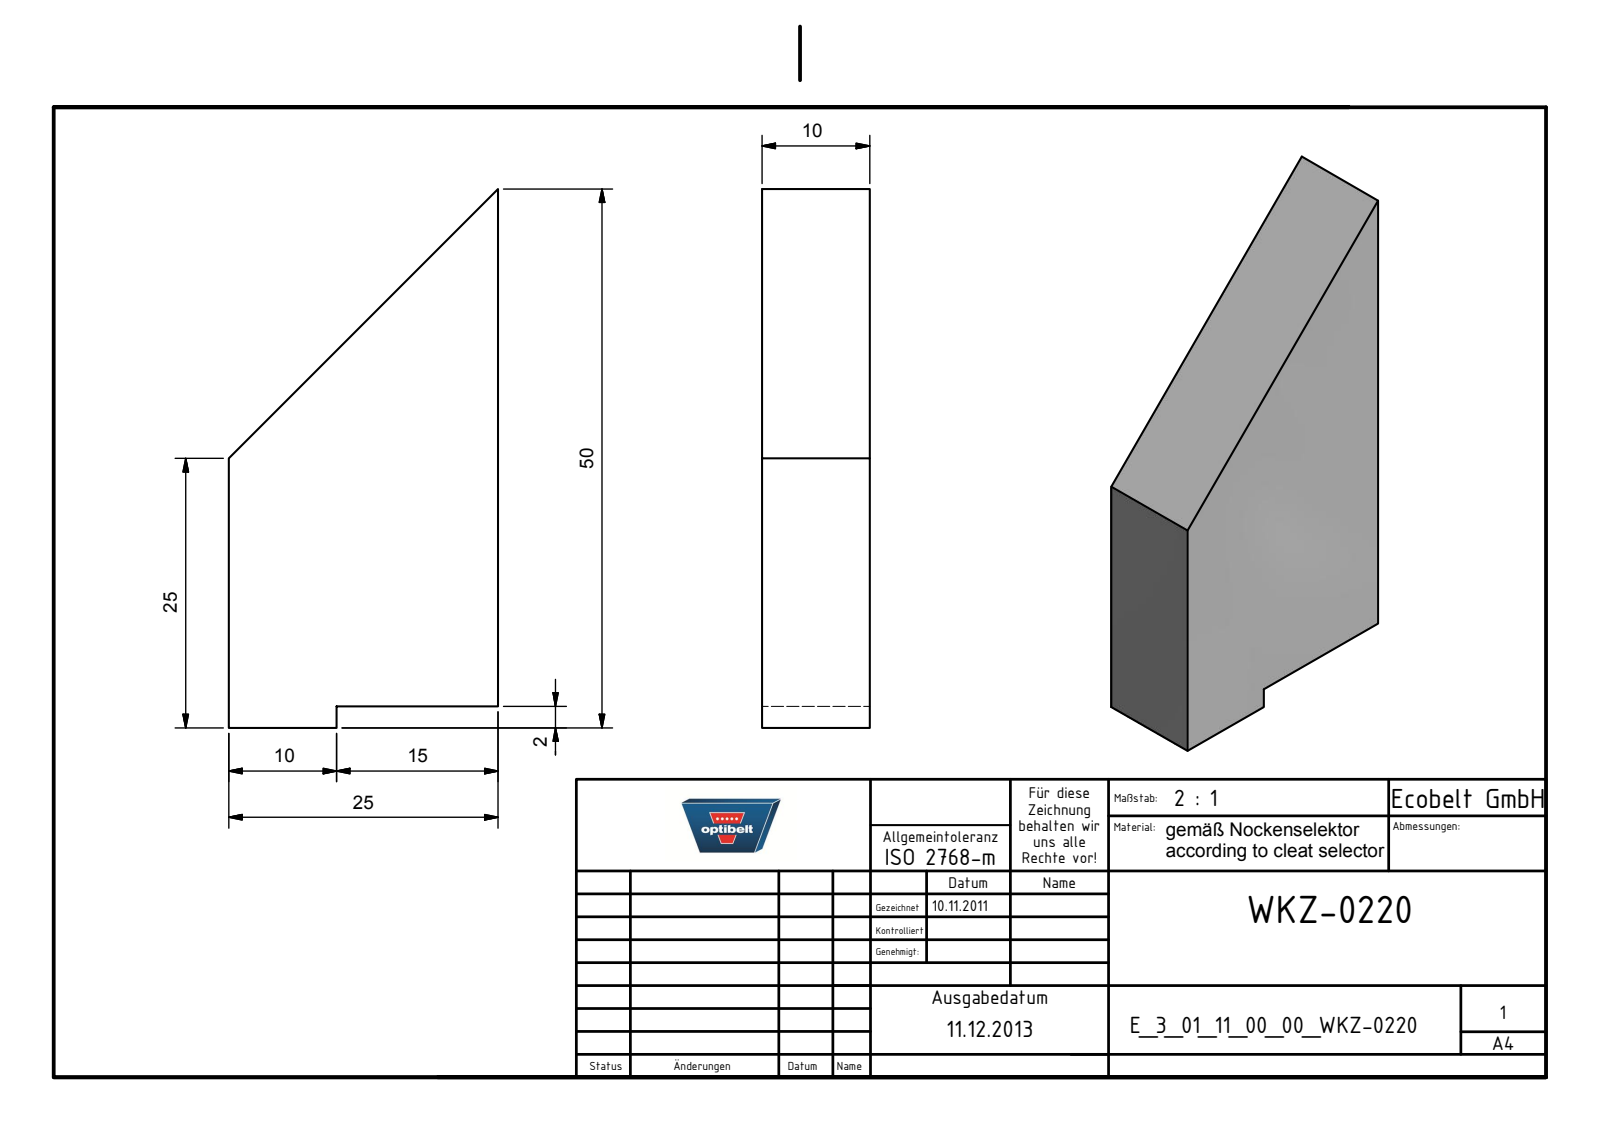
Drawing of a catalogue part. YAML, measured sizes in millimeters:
part_name: "E_3_01_11_00_00_WKZ-0220"
step_written_by: "Autodesk Inventor 2025 (AUTOMOTIVE_DESIGN)"
units: millimeters
bodies: {solids: 1, faces: 8, planar: 8, cylindrical: 0, other: 0}
overall_size: [50, 25, 10]
volume: 9075
surface_area: 3169
face_to_face_distances: [10, 25, 2, 15]
